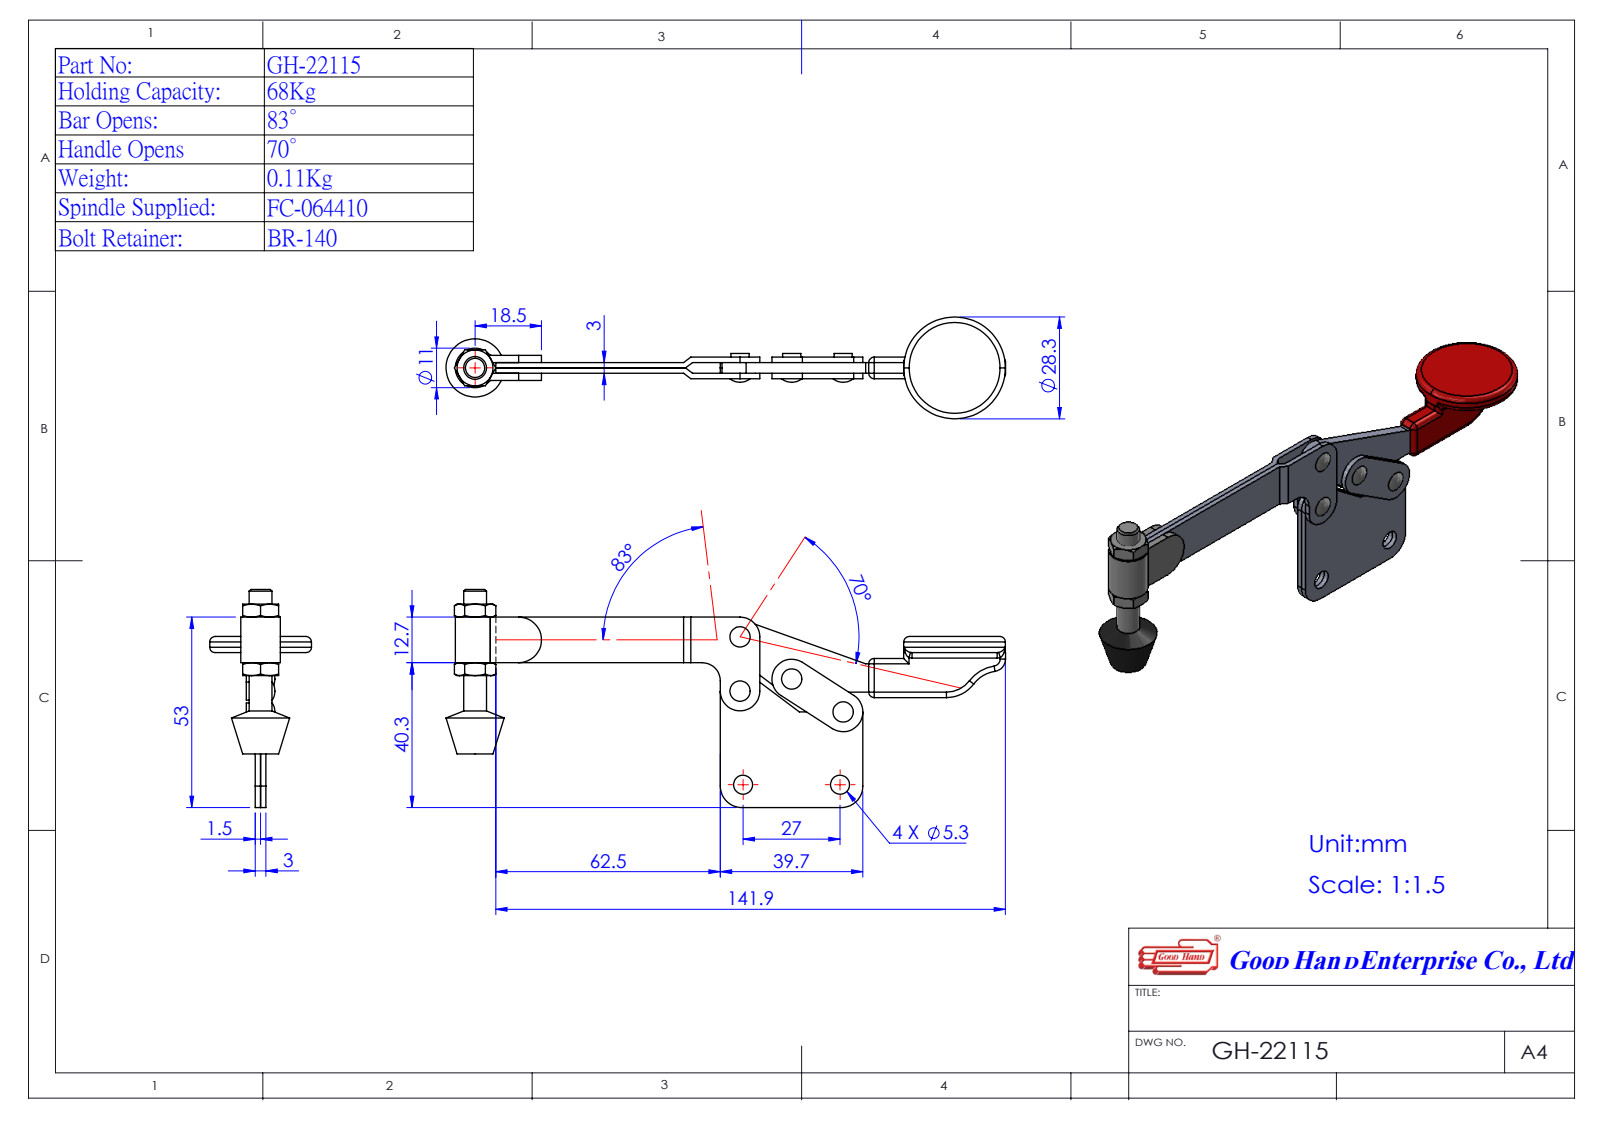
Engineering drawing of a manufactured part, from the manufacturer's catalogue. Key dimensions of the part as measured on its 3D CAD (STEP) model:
Part name (STEP PRODUCT): Group2^GH-22115(簡化)-1; Group1^GH-22105(簡化); 12210001-1^GH-22115(簡化)-1; Group1^GH-22115(簡化) (+2 more)
STEP written by: SolidWorks 2016 (AUTOMOTIVE_DESIGN)
Units: millimetres
Bodies: 5 solids, 240 faces (102 planar, 92 cylindrical, 46 other)
Overall size (bounding box): 157.15 × 60.4 × 28.32
Volume: 18 617 mm³ · Surface area: 16 552 mm²
Round holes (diameter × count): ⌀3 ×4, ⌀5.3 ×2, ⌀5 ×1, ⌀6 ×1
Round bosses / shafts (diameter × count): ⌀5.05 ×2, ⌀4.05 ×2, ⌀28.32 ×1, ⌀11 ×1, ⌀6.35 ×1
Partial cylindrical surfaces — rounded edges, fillets, slot ends (radius × count): R5.5 ×4, R2.02 ×2, R3.5 ×2, R5 ×2, R6 ×2, R4.5 ×1, R6.35 ×1, R9.13 ×1
Main face-to-face distances: 3, 1.5, 4.5, 6, 2, 3.5, 5, 6.5, 0.5, 12.7
Hole centre spacings: 14.87, 15.1, 17, 18.37, 20.27, 25.76, 27, 29.22
